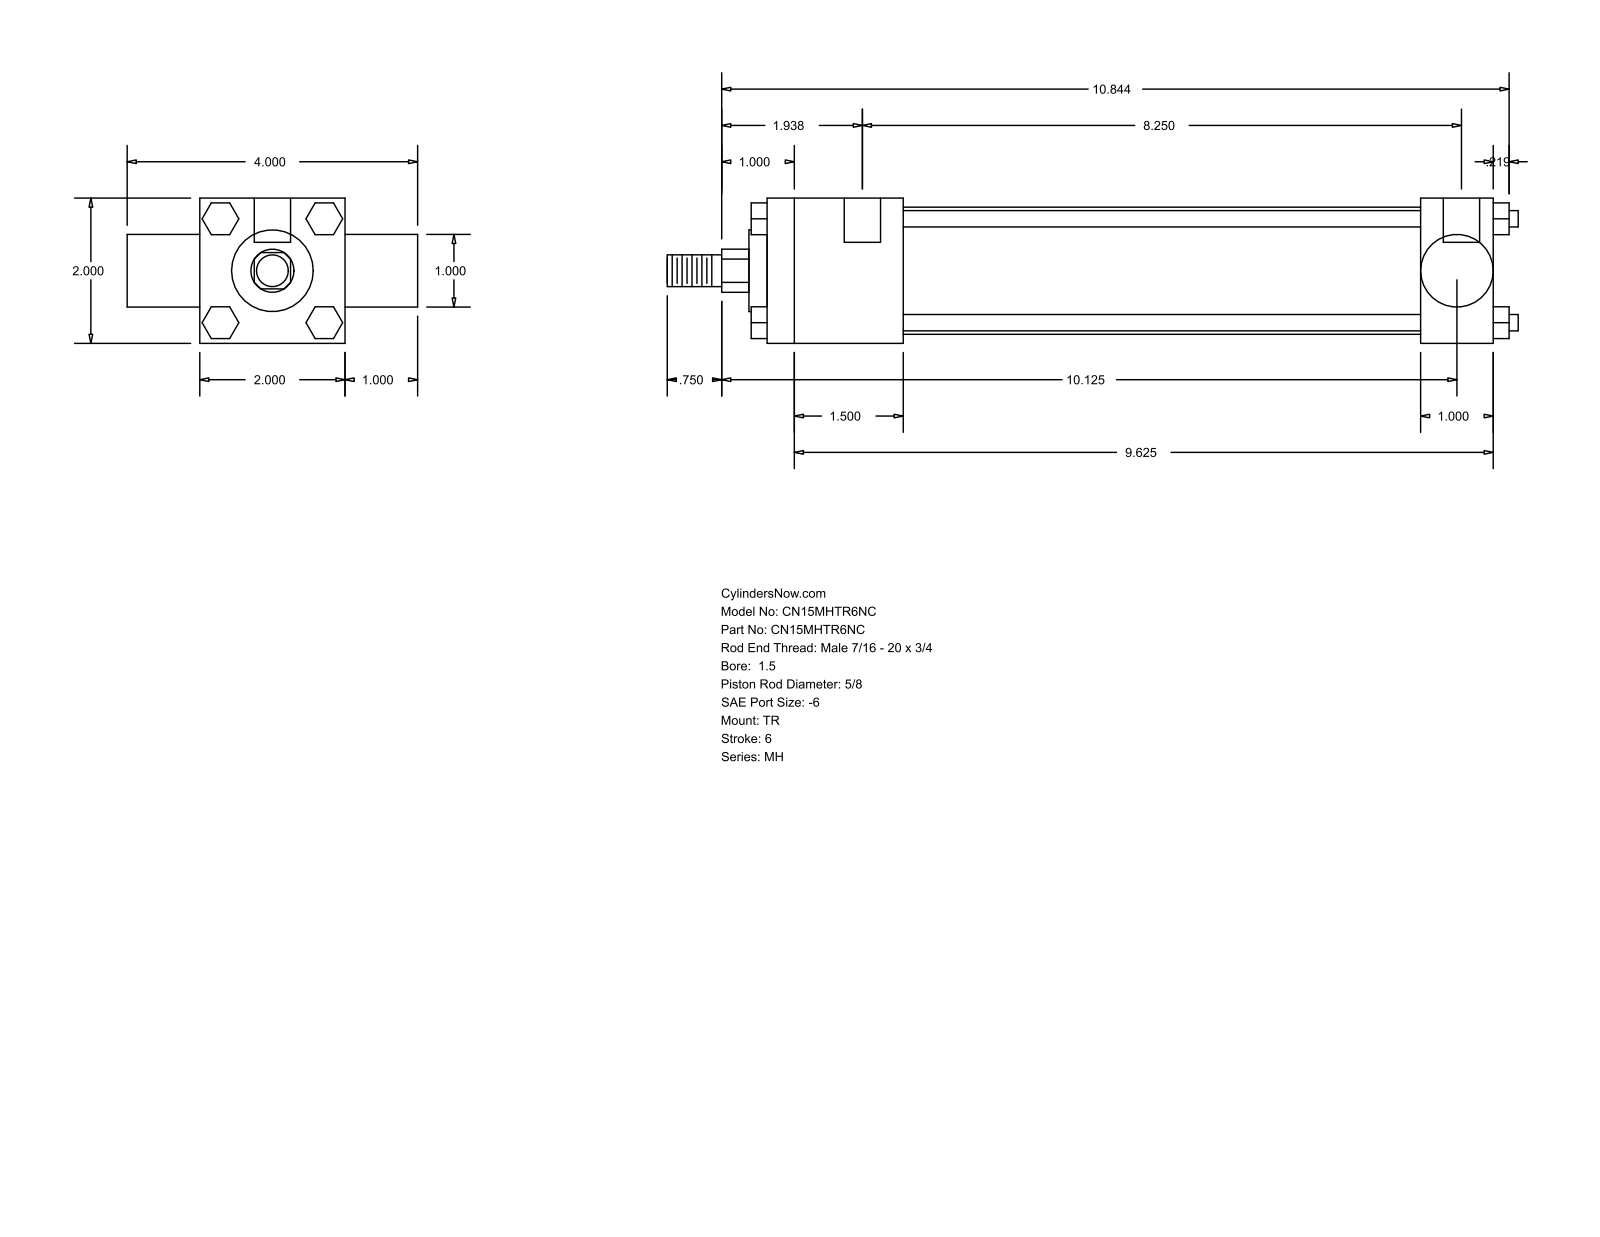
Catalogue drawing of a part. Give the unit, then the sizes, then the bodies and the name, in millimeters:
Units: millimetres
Overall size (bounding box): 297.66 × 101.6 × 50.8
Round holes (diameter × count): ⌀5.56 ×3, ⌀12.7 ×2
Round bosses / shafts (diameter × count): ⌀5.71 ×4, ⌀44.45 ×1, ⌀28.57 ×1, ⌀25.35 ×1, ⌀15.88 ×1, ⌀11.11 ×1
Partial cylindrical surfaces — rounded edges, fillets, slot ends (radius × count): R7.54 ×1
Main face-to-face distances: 50.8, 254, 25.4, 76.2, 47.62, 206.38, 228.59, 180.97, 25.41, 11.11
Hole centre spacings: 3.17, 209.55, 212.72
Bodies: 0 solids, 120 faces (92 planar, 28 cylindrical, 0 other)
Part name (STEP PRODUCT): MH_TR__0150_0.625
STEP written by: GSSL Pune (CONFIG_CONTROL_DESIGN)
